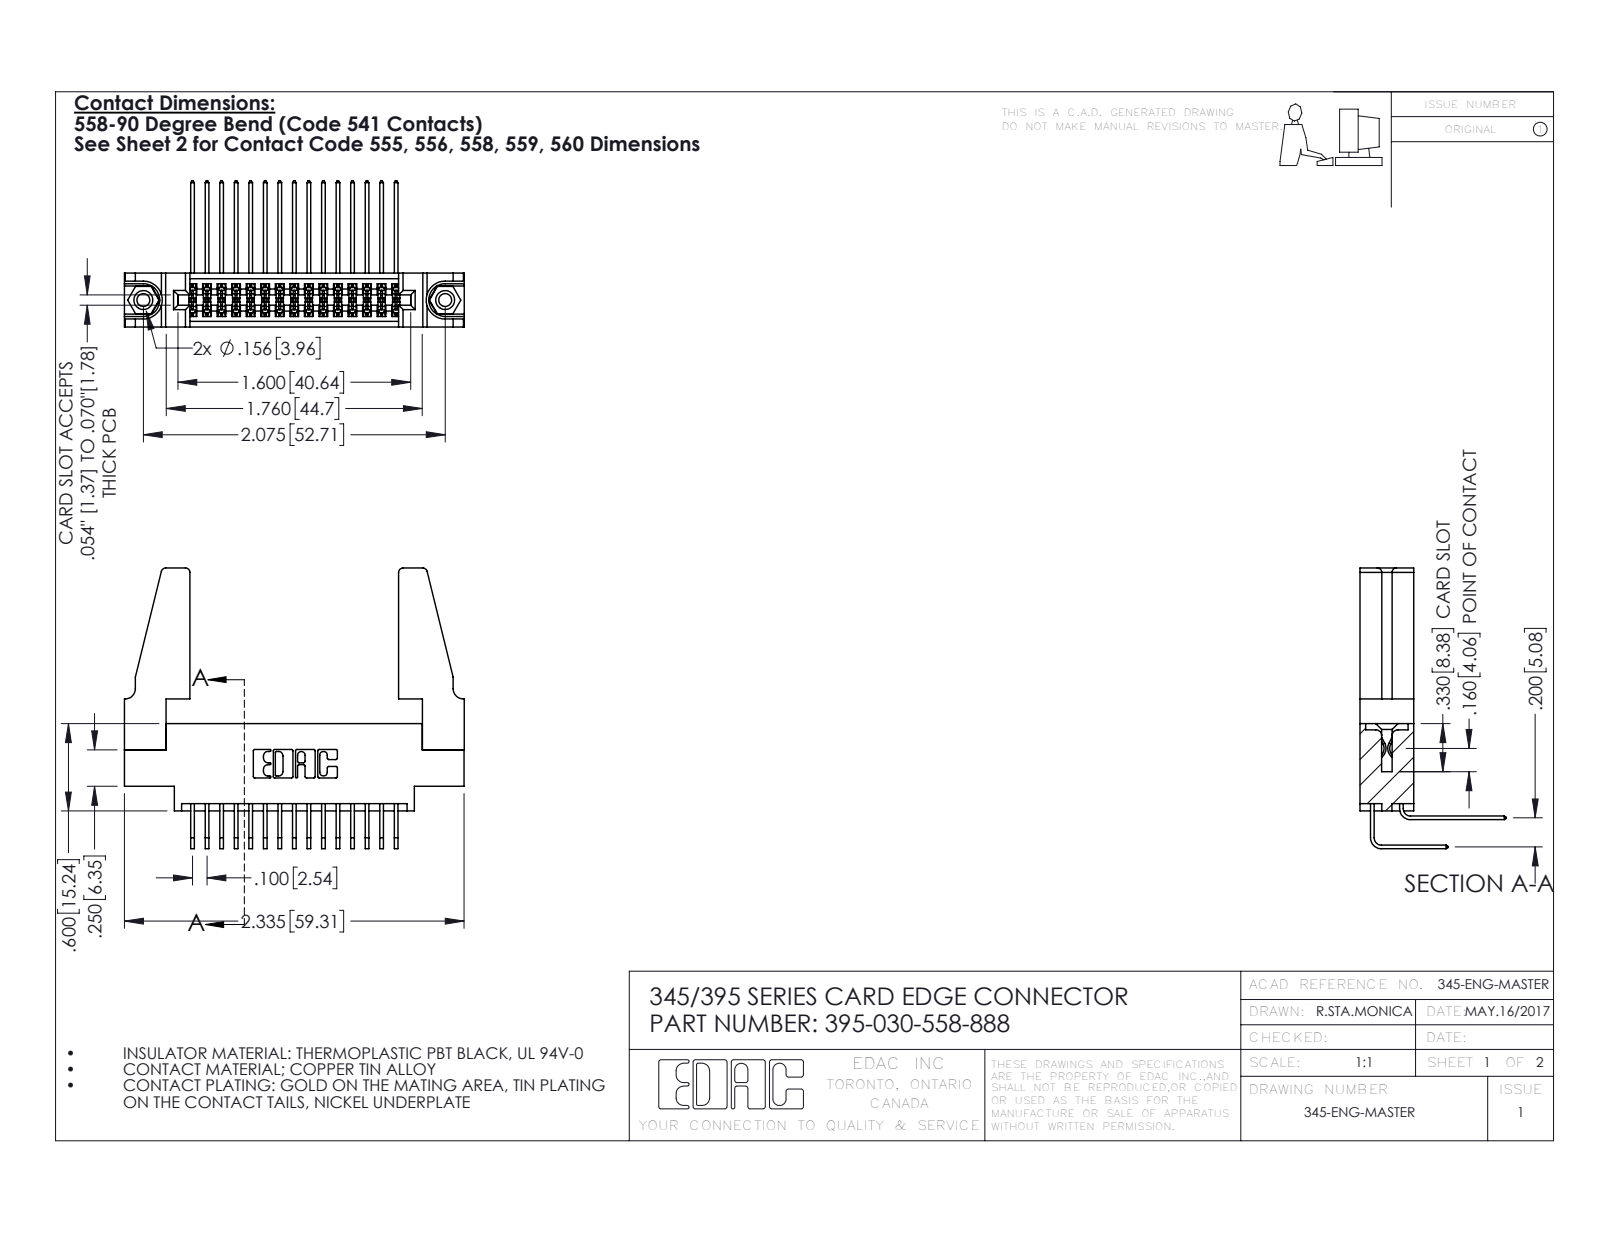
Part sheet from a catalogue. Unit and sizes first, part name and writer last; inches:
Units: inches
Overall size (bounding box): 2.336 × 1.929 × 1.005
Round holes (diameter × count): ⌀0.089 ×2, ⌀0.125 ×2, ⌀0.156 ×2, ⌀0.064 ×1
Round bosses / shafts (diameter × count): ⌀0.155 ×2
Partial cylindrical surfaces — rounded edges, fillets, slot ends (radius × count): R0.006 ×46, R0.01 ×22, R0.03 ×8, R0.007 ×6, R0.031 ×6, R0.026 ×3, R0.014 ×2, R0.019 ×2
Main face-to-face distances: 0.37, 0.072, 0.298, 0.2, 0.098, 0.272, 0.025, 0.225, 0.175, 0.148
Hole centre spacings: 0.27, 1.842, 2.075
Volume: 0.539 in³ · Surface area: 18.28 in²
Bodies: 35 solids, 1814 faces (1206 planar, 592 cylindrical, 16 other)
Part name (STEP PRODUCT): 395-030-558-888; 345-220-078_345-220-088; 345-250-001_345-250-001-102; 345 Part_0.170 Offset - 0.156 Dia-TH (+2 more)
STEP written by: SolidWorks 2016 (CONFIG_CONTROL_DESIGN)
